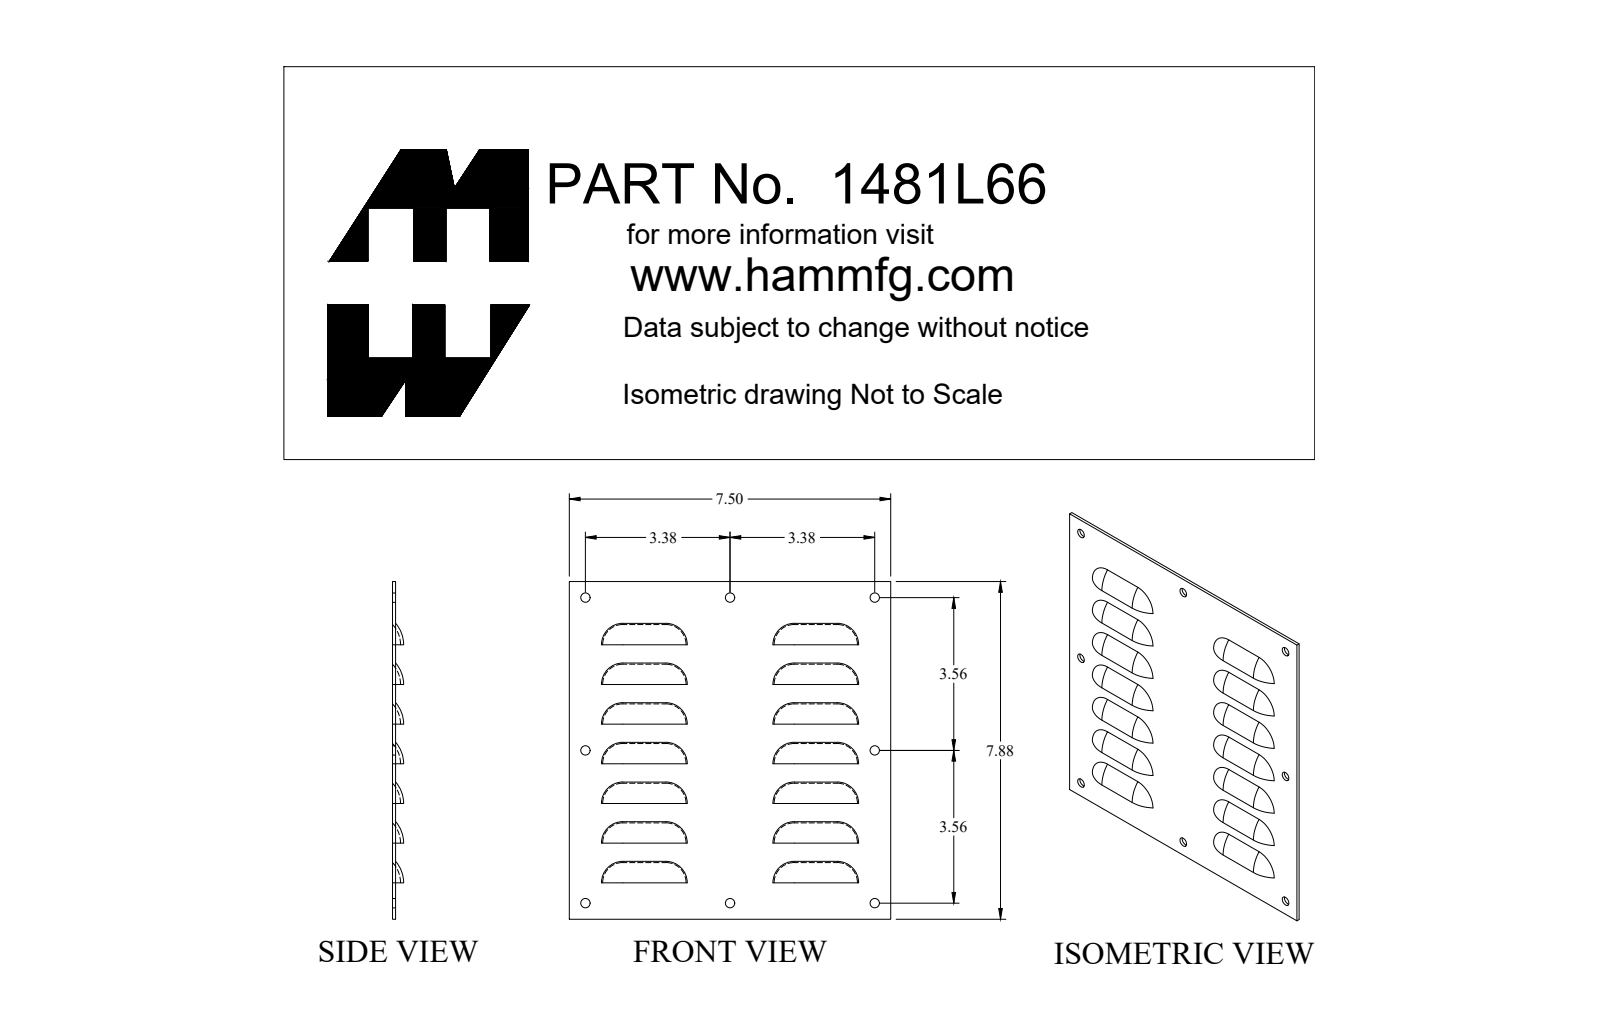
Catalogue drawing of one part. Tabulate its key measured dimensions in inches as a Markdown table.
| quantity | value |
| --- | --- |
| part name | 1481L66_Default |
| STEP written by | SolidWorks 2019 (CONFIG_CONTROL_DESIGN) |
| units | inches |
| bodies | 1 solid, 134 faces (34 planar, 44 cylindrical, 56 other) |
| overall size | 7.875 × 7.5 × 0.259 |
| volume | 4.333 in³ |
| surface area | 126.8 in² |
| round holes (diameter × count) | 0.218 × 8 |
| partial cylindrical surfaces (radius × count) | 0.69 × 7, 0.762 × 7 |
| main face-to-face distances | 0.072, 1.85, 3.7, 0.925, 0.925, 2.775, 2.775, 7.5, 5.55, 4.625 |
| hole center spacings | 3.375, 3.563, 4.907, 7.632, 7.884, 6.75, 7.125, 9.815 |
